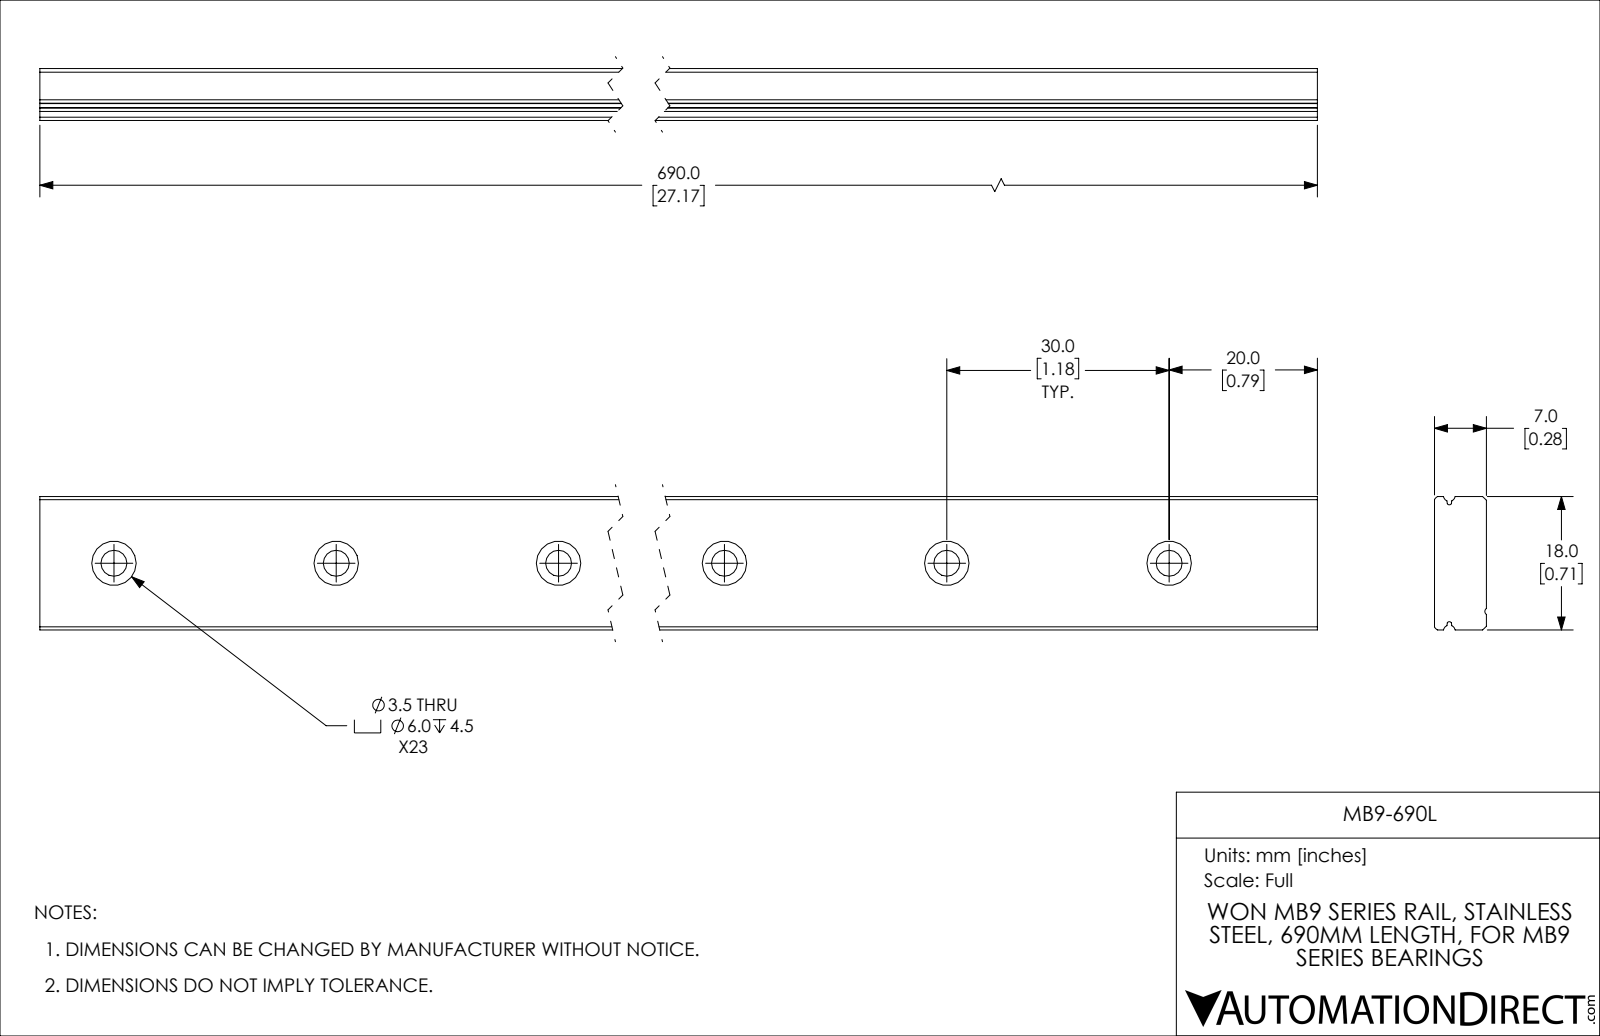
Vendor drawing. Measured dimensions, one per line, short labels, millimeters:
name: MB9-690L
written by: SolidWorks 2019 (CONFIG_CONTROL_DESIGN)
unit: mm
bodies: 1 solid, 140 faces (38 planar, 102 cylindrical, 0 other)
size: 690 × 18 × 7
volume: 81 698 mm³; area: 38 179 mm²
holes: 23× ⌀3.5, 23× ⌀6
rounds: 2× R0.32, 2× R0.8, 2× R0.95, 1× R0.5
face distances: 7, 18, 1.63, 2.5, 4.5, 690
hole spacings: 30, 60, 90, 120, 150, 180, 210, 240
